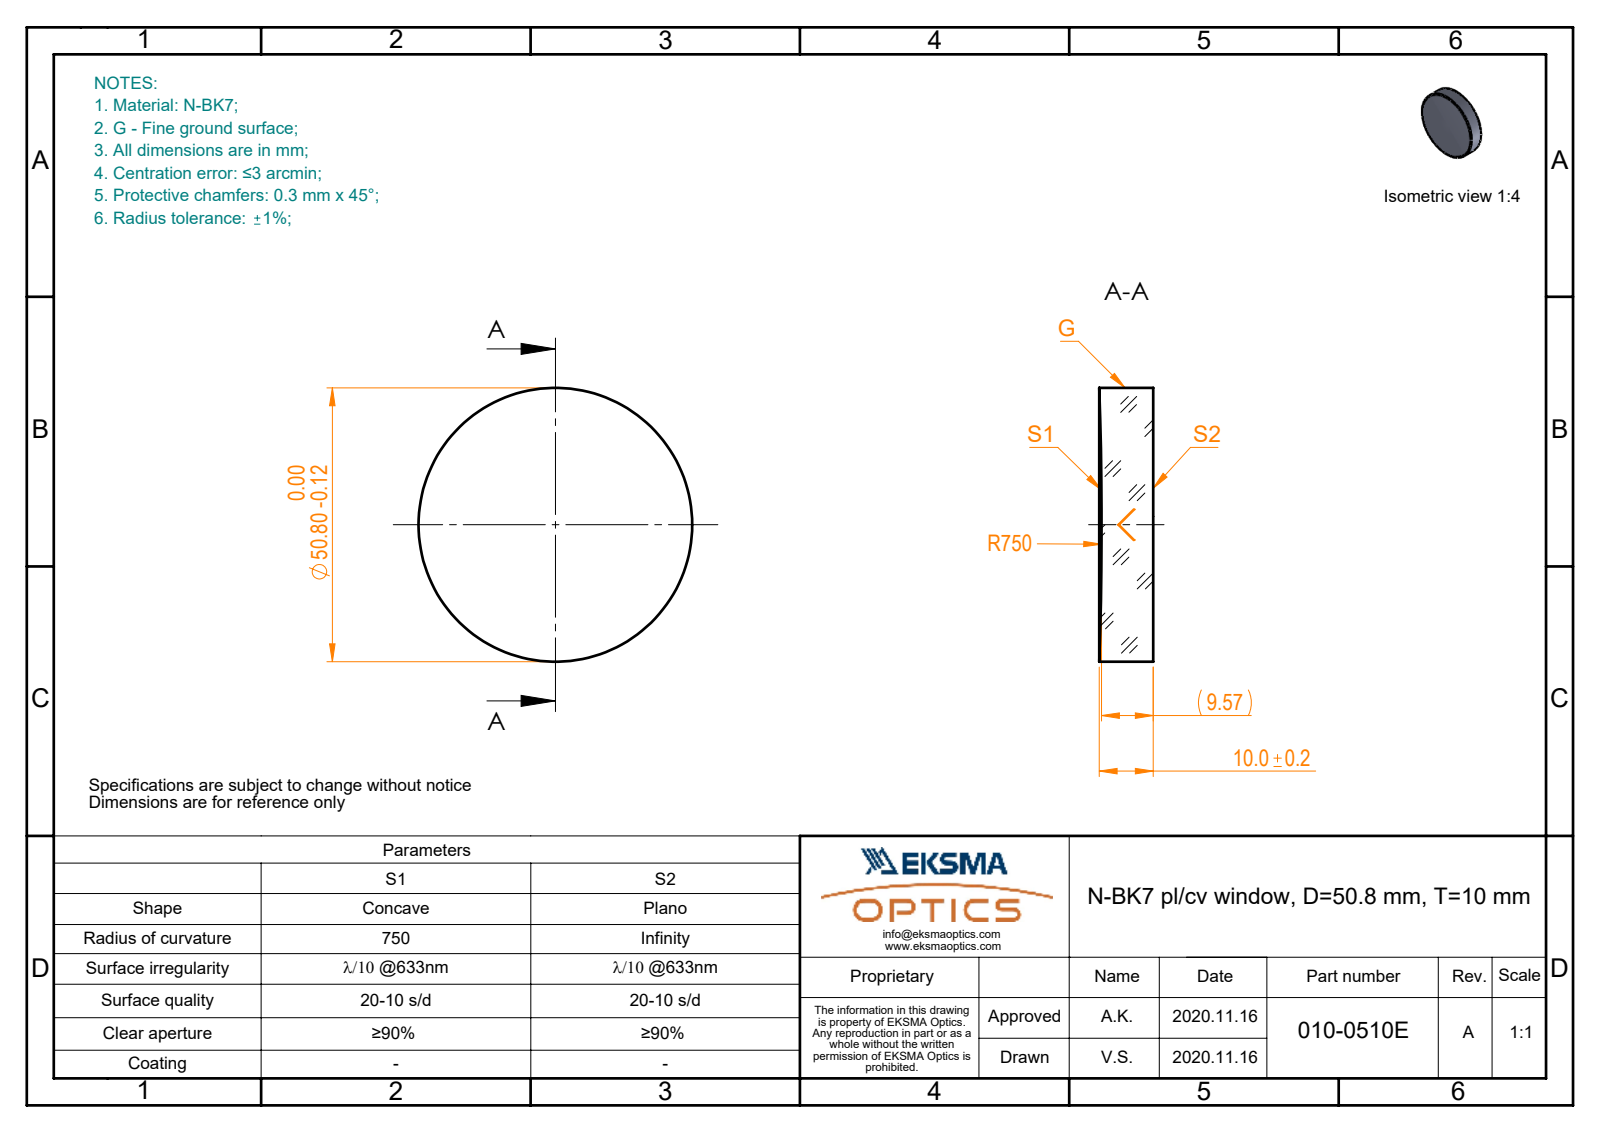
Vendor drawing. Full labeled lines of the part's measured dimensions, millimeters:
Part name (STEP PRODUCT): 010-0510E_N-BK7_PCV_window
STEP written by: SolidWorks 2019 (CONFIG_CONTROL_DESIGN)
Units: millimetres
Bodies: 1 solid, 5 faces (1 planar, 2 cylindrical, 2 other)
Overall size (bounding box): 50.8 × 50.8 × 10
Volume: 19 832 mm³ · Surface area: 5 650 mm²
Round bosses / shafts (diameter × count): ⌀50.8 ×1
